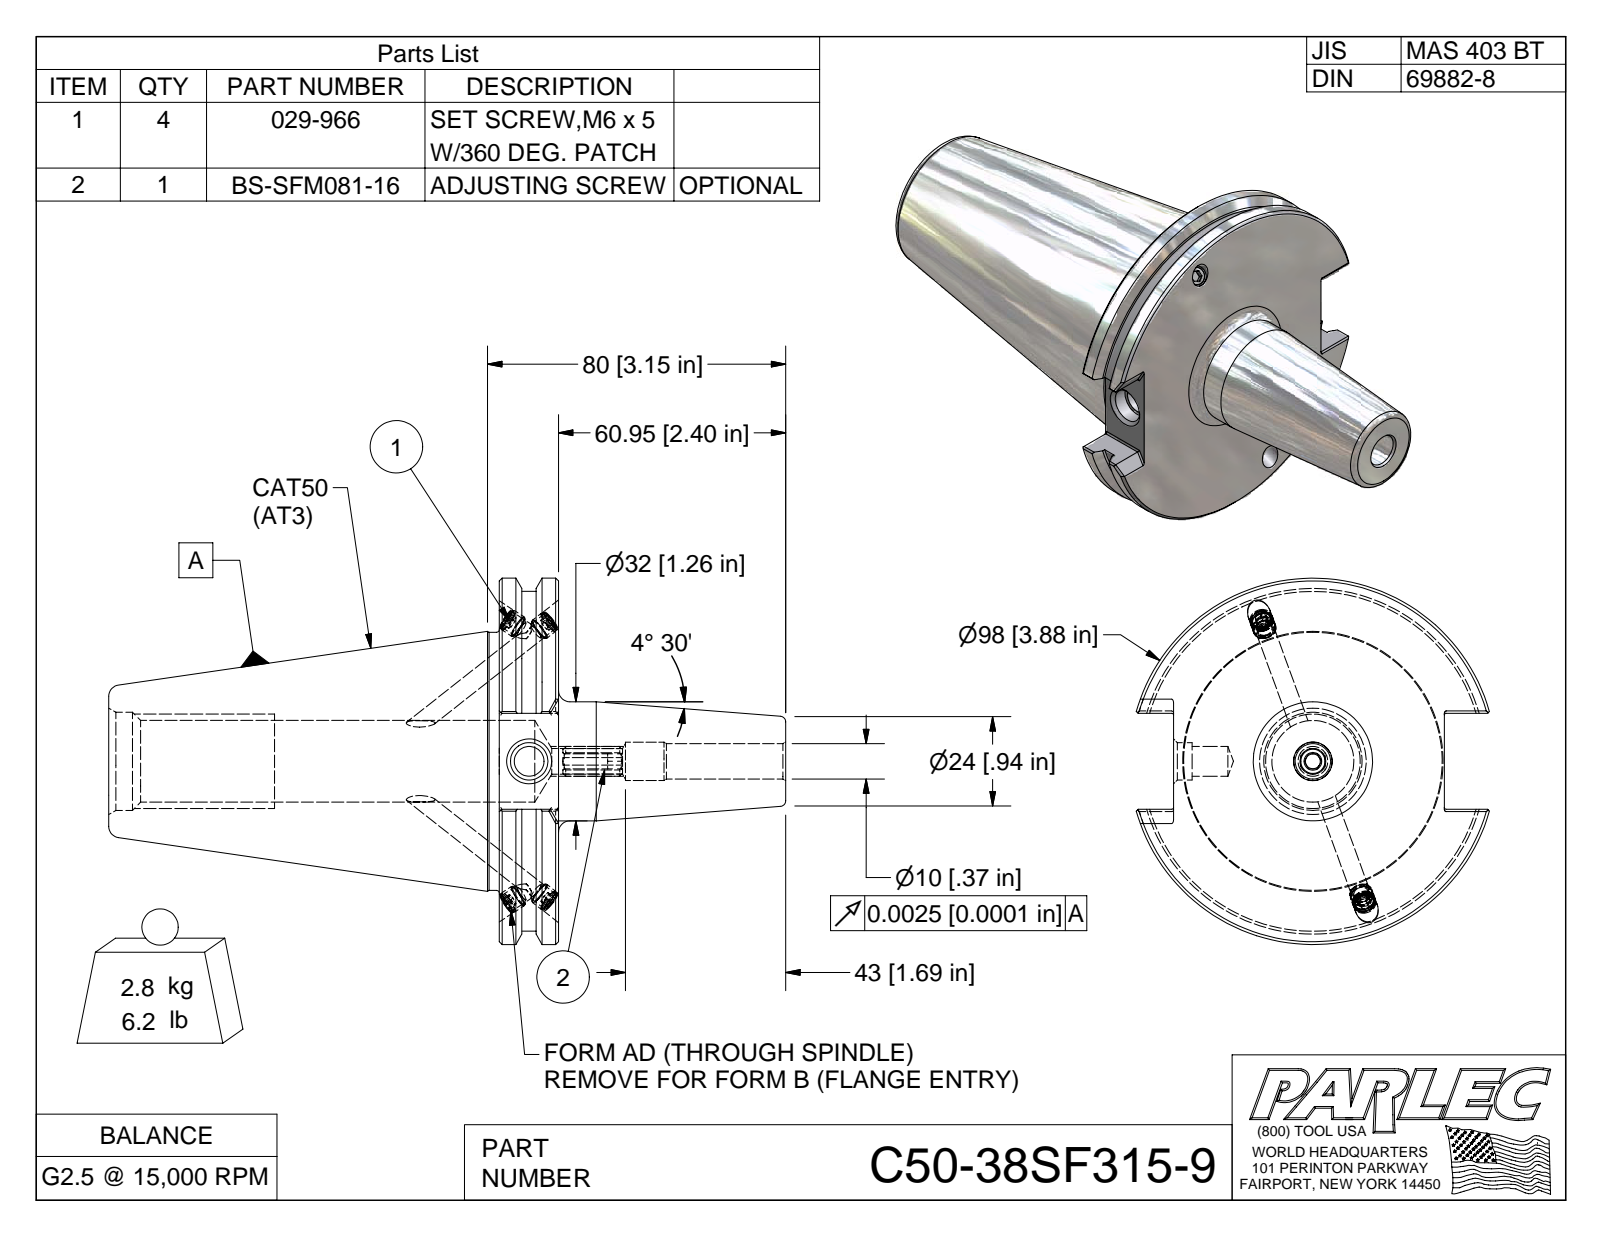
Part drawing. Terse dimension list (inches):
name: C50-38SF315-9; C50BC-38SF315-9-1; BS-SFM081-16; 029-966
written by: Autodesk Inventor 2009 (AUTOMOTIVE_DESIGN)
unit: in
bodies: 6 solids, 184 faces (87 planar, 44 cylindrical, 53 other)
size: 7.15 × 3.875 × 3.729
volume: 21.57 in³; area: 83.38 in²
holes: 4× ⌀0.197, 4× ⌀0.24, 1× ⌀0.374, 1× ⌀0.404
bosses: 4× ⌀0.244, 4× ⌀0.236, 1× ⌀3.875, 1× ⌀3.594, 1× ⌀2.73, 1× ⌀1.26
rounds: 12× R0.02, 1× R0.157
face distances: 0.625, 4.125, 4.75, 2.86, 7.15, 3.025, 2.4, 1.015, 4.363, 0.238
